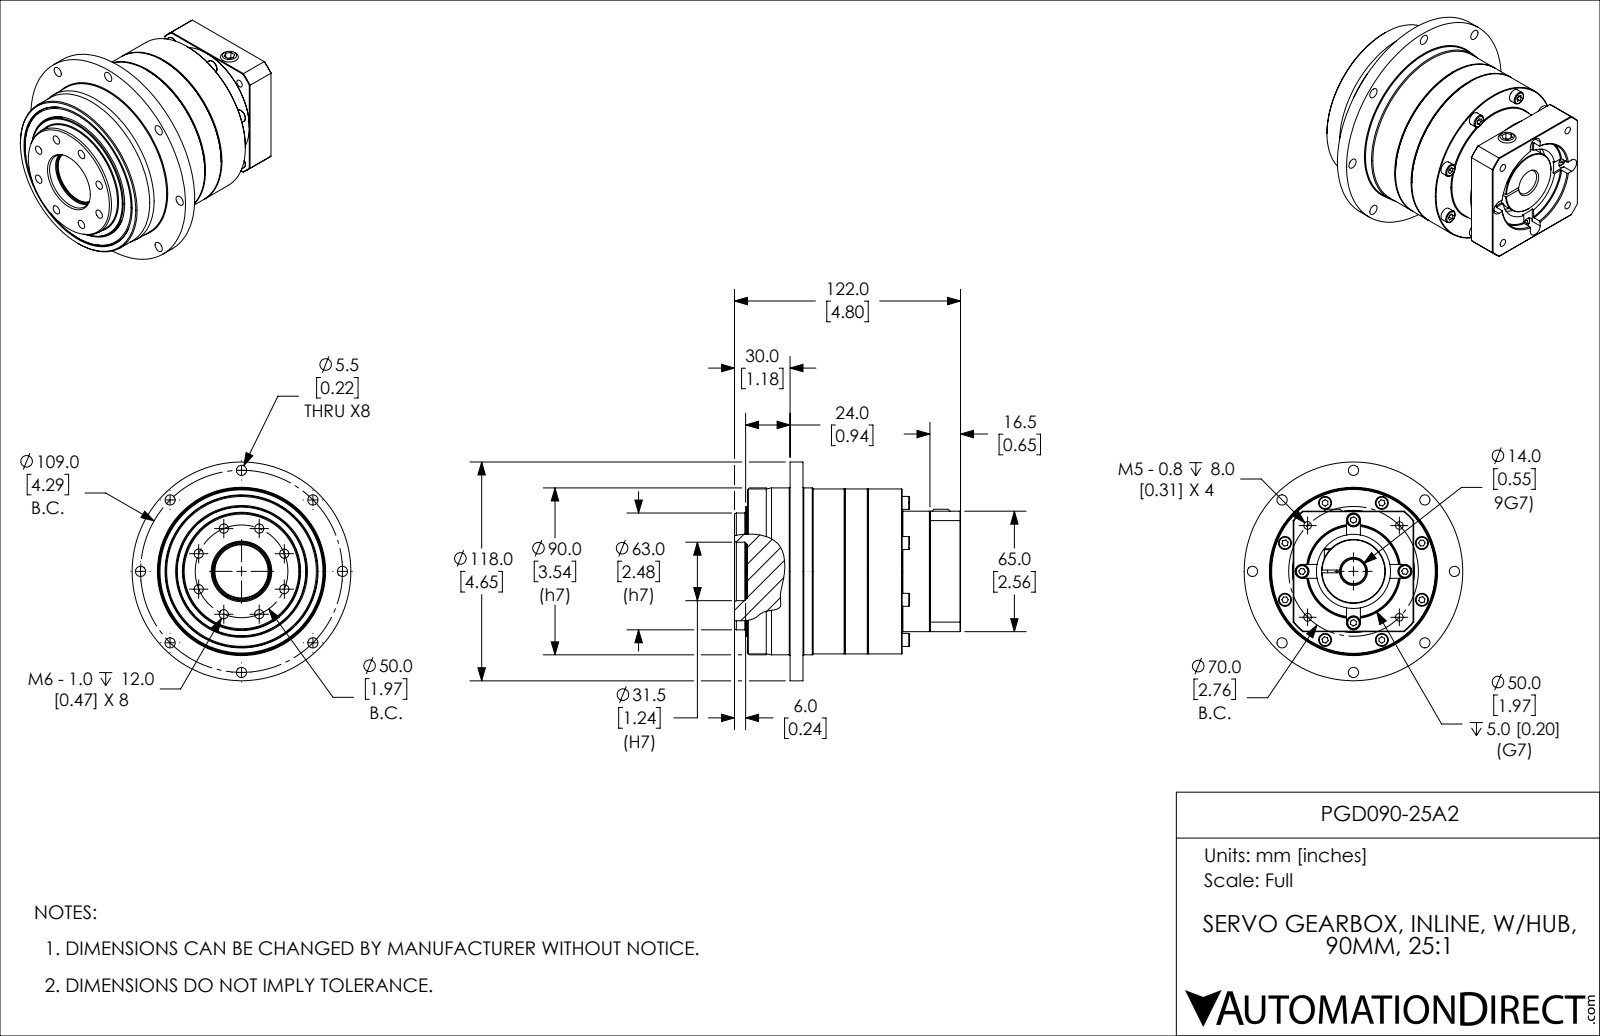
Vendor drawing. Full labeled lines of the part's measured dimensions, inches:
Part name (STEP PRODUCT): PGD090-25A2
STEP written by: SolidWorks 2015 (AUTOMOTIVE_DESIGN)
Units: inches
Bodies: 5 solids, 502 faces (259 planar, 150 cylindrical, 93 other)
Overall size (bounding box): 4.804 × 4.646 × 4.646
Volume: 41.04 in³ · Surface area: 116.5 in²
Round holes (diameter × count): ⌀0.217 ×8, ⌀0.194 ×7, ⌀0.163 ×4, ⌀0.197 ×4, ⌀0.295 ×4, ⌀0.194 ×1, ⌀0.315 ×1, ⌀0.335 ×1, ⌀0.551 ×1, ⌀0.709 ×1, ⌀0.787 ×1, ⌀1.24 ×1
Round bosses / shafts (diameter × count): ⌀0.276 ×12, ⌀4.646 ×1, ⌀3.543 ×1, ⌀3.504 ×1, ⌀2.559 ×1, ⌀2.48 ×1, ⌀1.654 ×1, ⌀1.26 ×1
Partial cylindrical surfaces — rounded edges, fillets, slot ends (radius × count): R0.187 ×1, R1.673 ×1
Main face-to-face distances: 0.157, 0.906, 1.063, 3.721, 2.383, 2.54, 3.446, 1.083, 3.465, 3.623
Hole centre spacings: 1.293, 2.681, 3.078, 0.984, 0.419, 0.601, 0.981, 1.157
